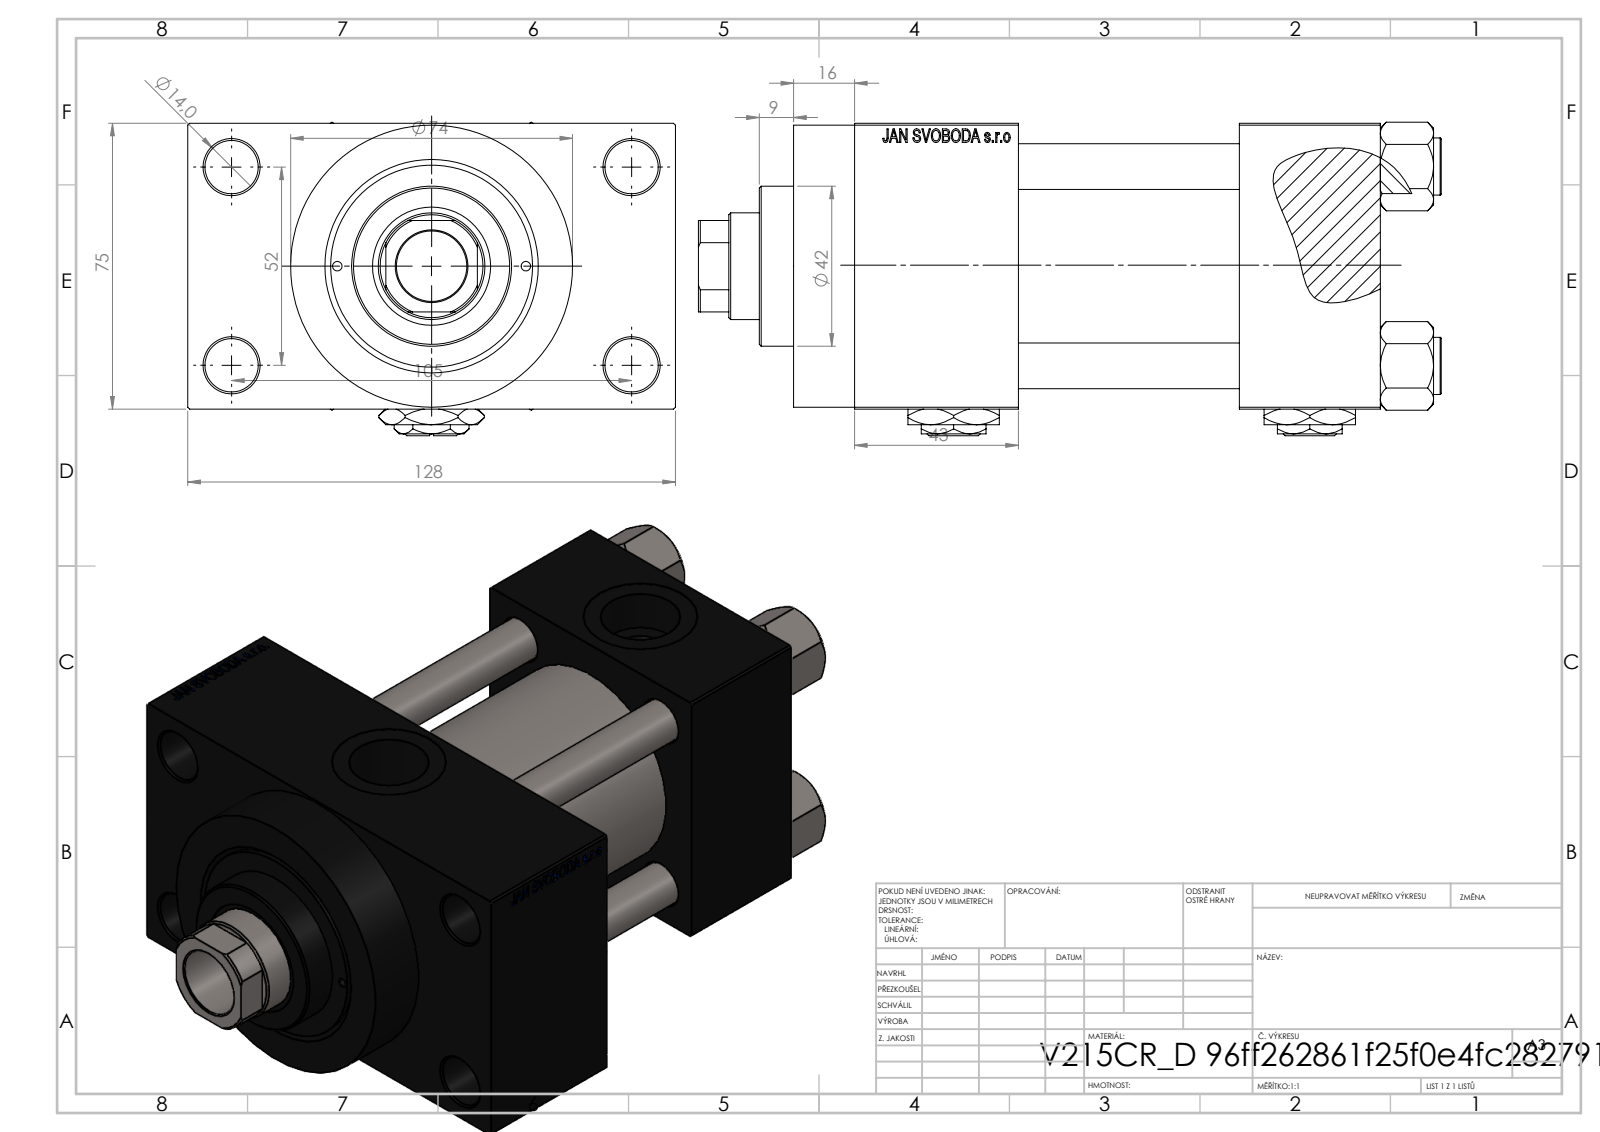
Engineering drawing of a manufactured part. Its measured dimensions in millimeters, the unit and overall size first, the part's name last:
Units: millimetres
Overall size (bounding box): 195 × 128 × 82.27
Round holes (diameter × count): ⌀12 ×4, ⌀14 ×4, ⌀2.5 ×2, ⌀7 ×2, ⌀20.96 ×2, ⌀30 ×2, ⌀18.5 ×1, ⌀28 ×1, ⌀31 ×1, ⌀41 ×1, ⌀50 ×1, ⌀53 ×1
Round bosses / shafts (diameter × count): ⌀15 ×4, ⌀74 ×1, ⌀56 ×1, ⌀42 ×1
Partial cylindrical surfaces — rounded edges, fillets, slot ends (radius × count): R13.5 ×1
Main face-to-face distances: 75, 58, 37, 95, 101.5, 26.5, 138, 101, 43, 16
Hole centre spacings: 26.19, 26.35, 36.98, 38.03, 52.3, 57.22, 58.43, 58.59
Volume: 810 628 mm³ · Surface area: 173 039 mm²
Bodies: 13 solids, 1213 faces (547 planar, 104 cylindrical, 562 other)
Part name (STEP PRODUCT): Zatka_pro_OIL_PORT; V215CR_VCP_D; V215CR_D_TYCINKA; NUT_M5_D (+2 more)
STEP written by: SolidWorks 2019 (CONFIG_CONTROL_DESIGN)
